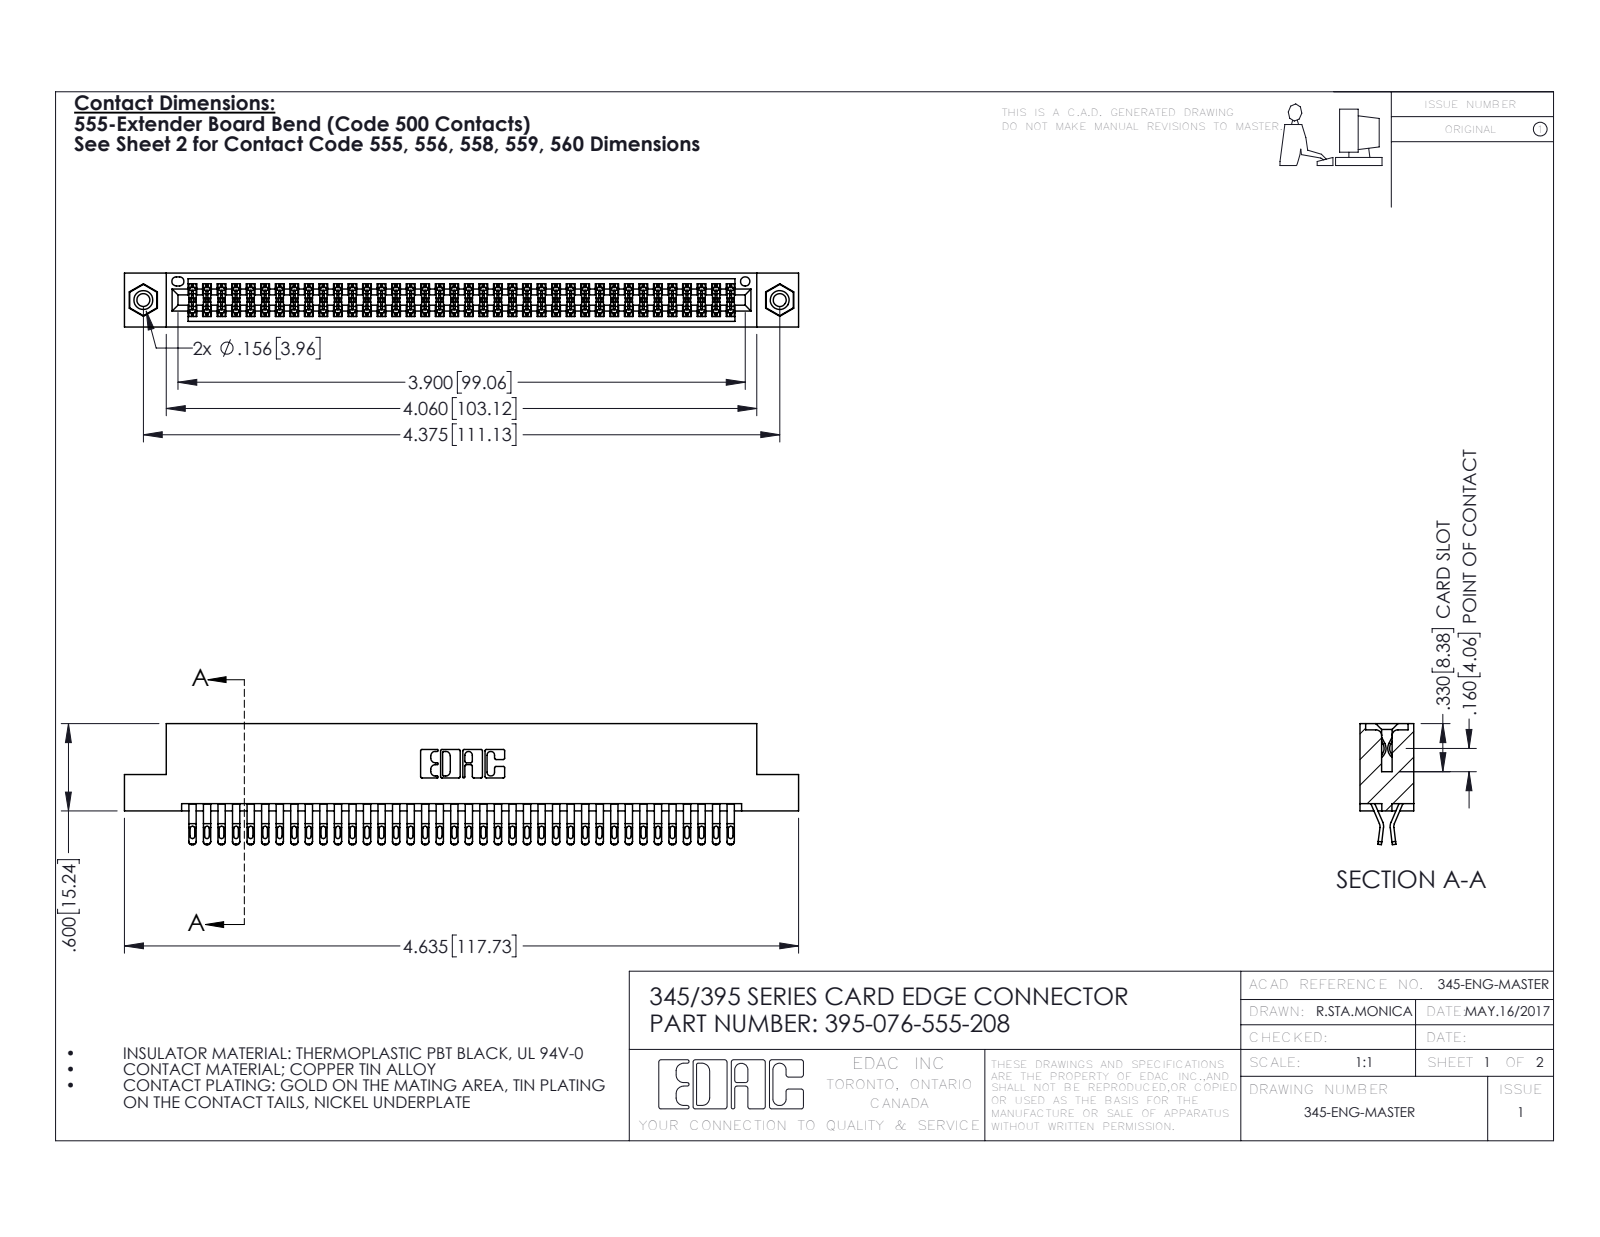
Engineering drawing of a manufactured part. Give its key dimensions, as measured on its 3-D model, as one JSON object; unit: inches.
{"part_name": "395-076-555-208; 345 Part_Flush Mounting Lugs - 0.156 Dia-TI; 345-250-001_345-250-003-102; 345-292-001_555 Tail", "step_written_by": "SolidWorks 2016 (CONFIG_CONTROL_DESIGN)", "units": "inches", "bodies": {"solids": 79, "faces": 4442, "planar": 2468, "cylindrical": 1958, "other": 16}, "overall_size": [4.635, 0.832, 0.37], "volume_in3": 0.709, "surface_area_in2": 27.7, "round_holes": [[0.089, 2], [0.125, 2], [0.156, 2], [0.064, 1]], "round_bosses_or_shafts": [[0.155, 2]], "partial_cylinders_radius": [[0.016, 190], [0.02, 152], [0.006, 114], [0.01, 22], [0.007, 6], [0.031, 6], [0.026, 3], [0.01, 2]], "face_to_face_distances": [0.072, 0.298, 0.2, 0.025, 0.37, 0.098, 0.272, 0.225, 0.175, 0.149], "hole_center_spacings": [0.27, 4.139, 4.375]}
